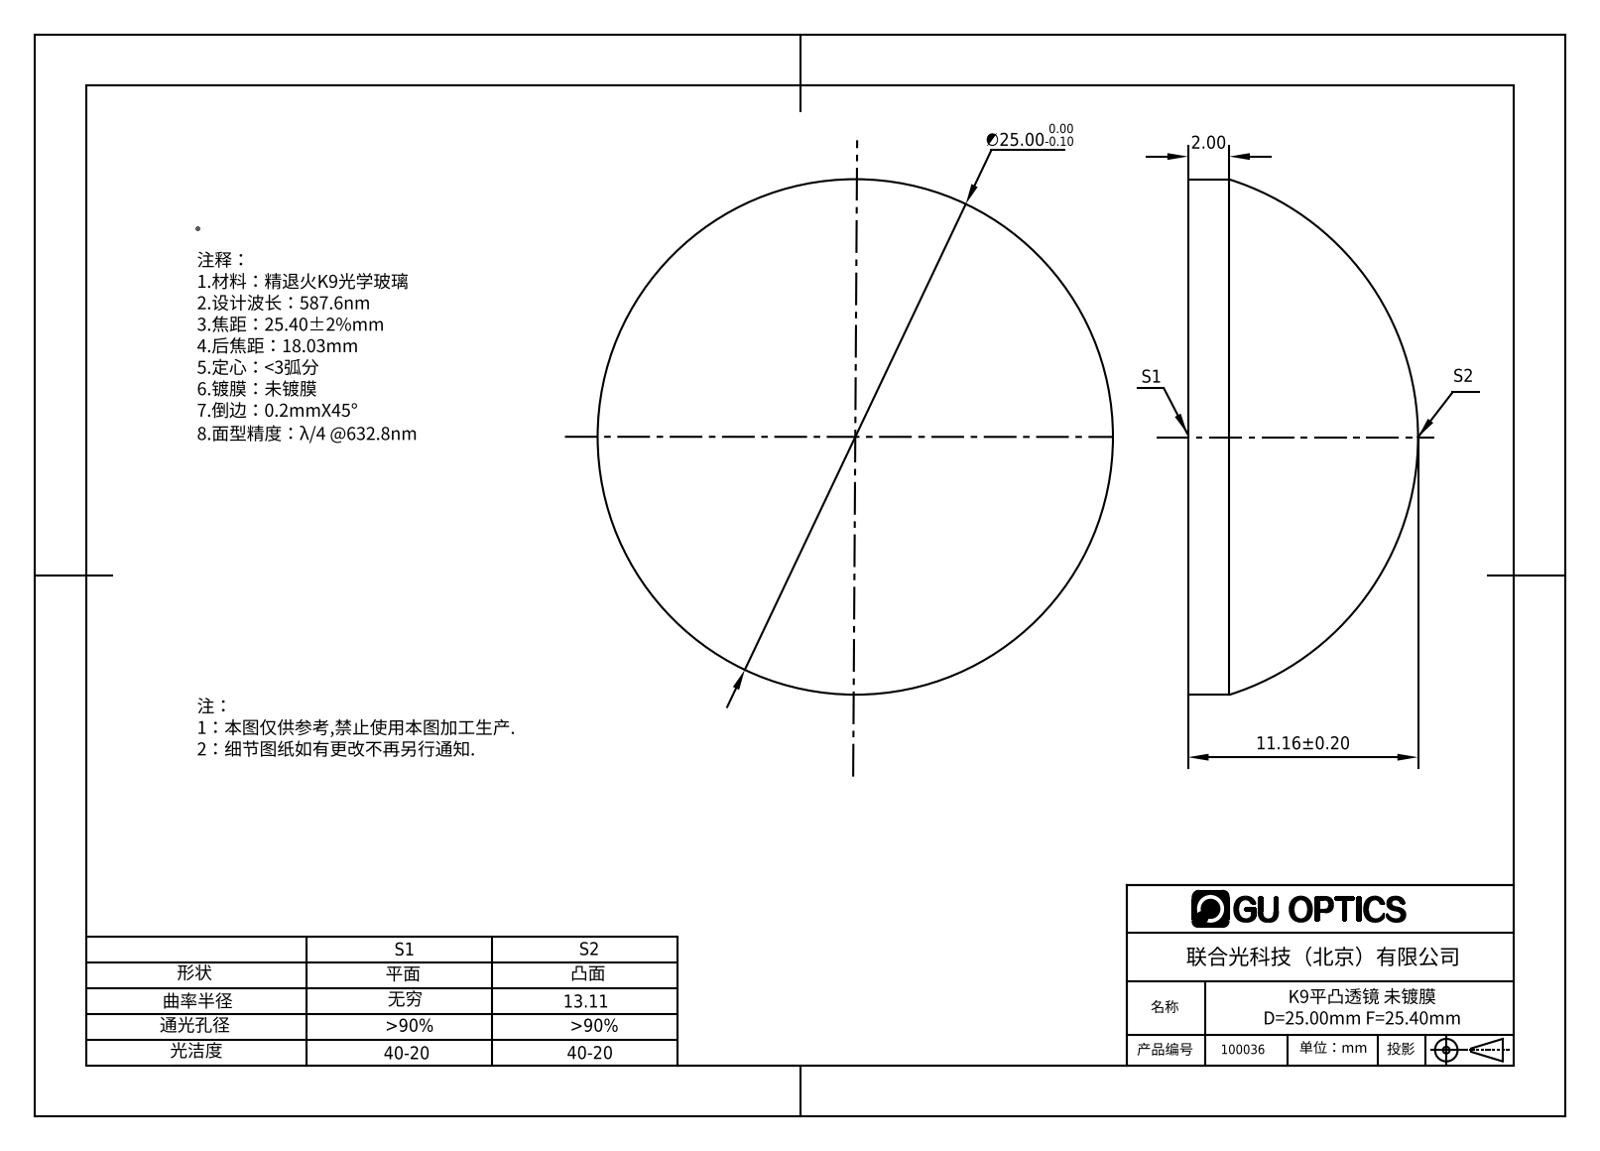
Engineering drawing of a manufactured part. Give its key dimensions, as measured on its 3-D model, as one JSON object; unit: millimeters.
{"part_name": "100036", "step_written_by": "SolidWorks 2016 (AUTOMOTIVE_DESIGN)", "units": "millimeters", "bodies": {"solids": 1, "faces": 5, "planar": 1, "cylindrical": 2, "other": 2}, "overall_size": [25, 25, 11.16], "volume_mm3": 3632, "surface_area_mm2": 1402, "round_bosses_or_shafts": [[25, 1]]}
